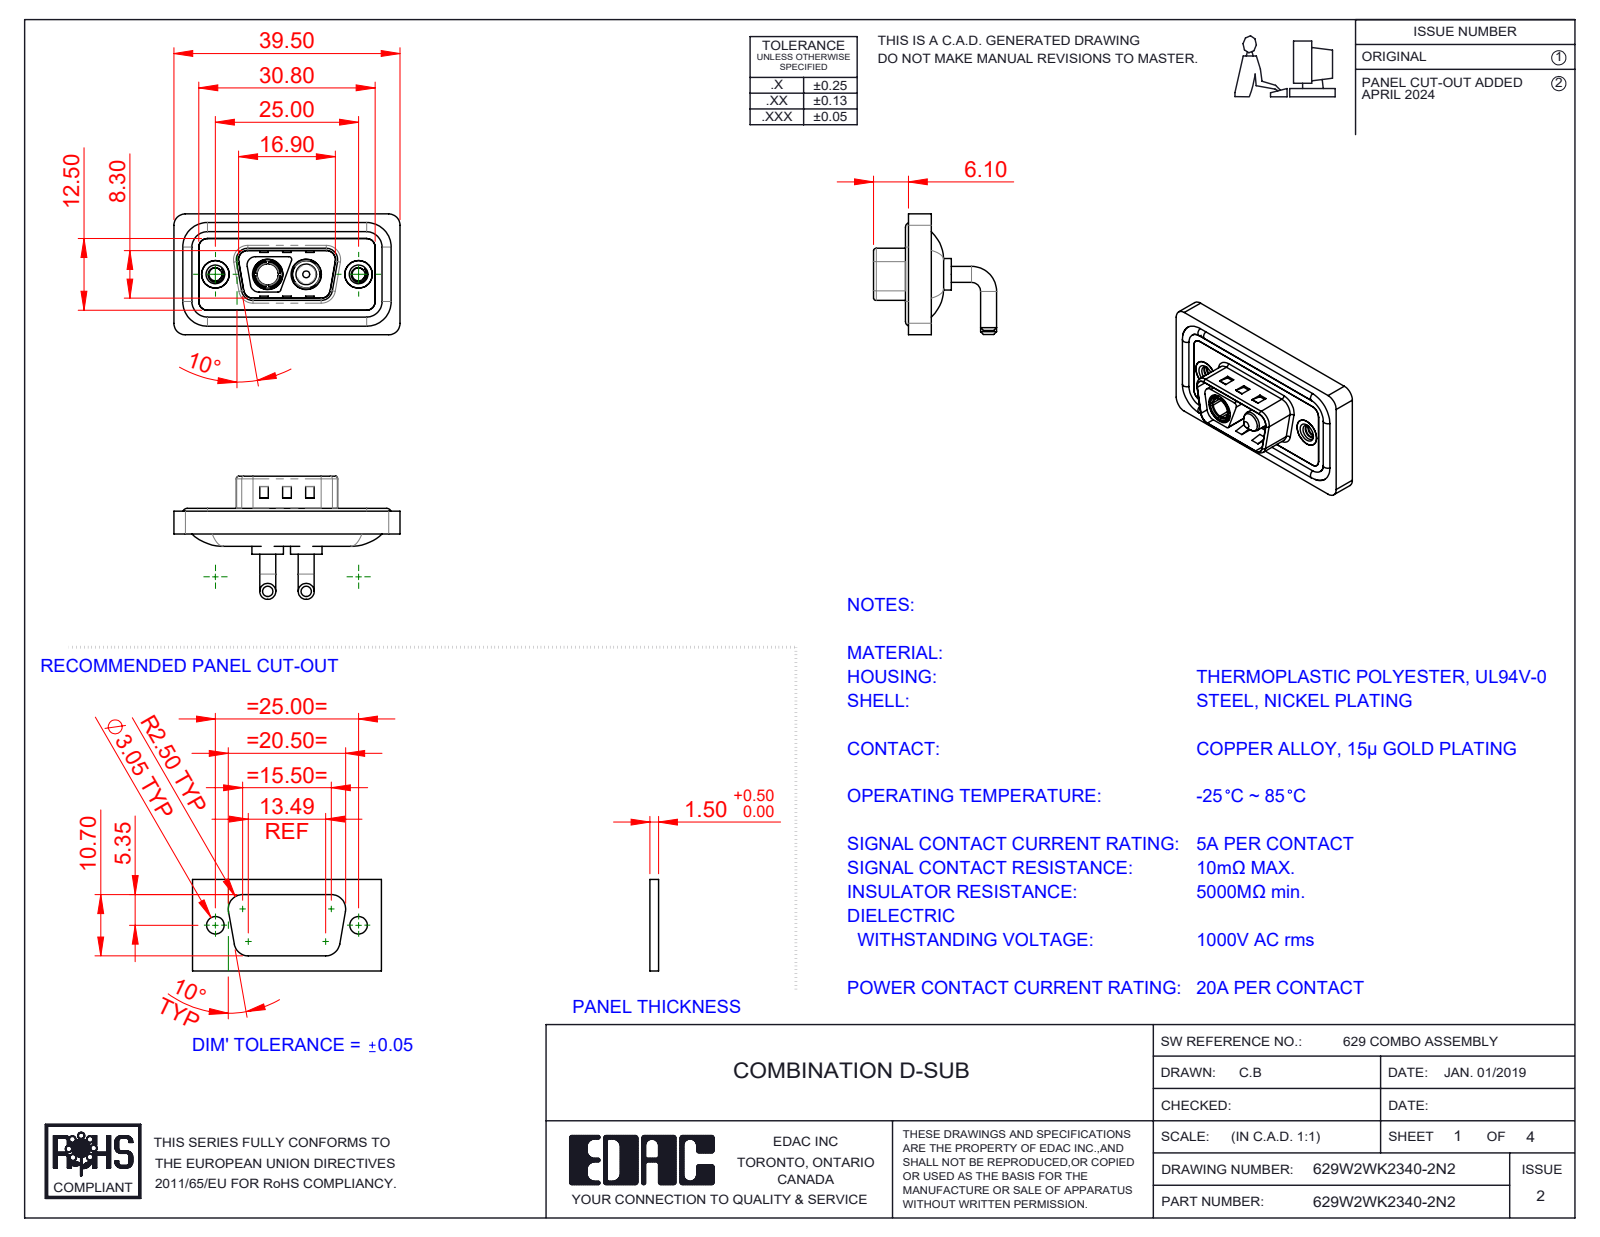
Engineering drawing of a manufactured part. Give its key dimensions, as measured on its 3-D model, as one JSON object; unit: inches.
{"part_name": "629W2WK2340-2N2; 629Combo Threaded Rivet_2; Power Pin_20A RA; 629Combo Waterproof Housing_09 Contacts (+4 more)", "step_written_by": "SolidWorks 2023 (CONFIG_CONTROL_DESIGN)", "units": "inches", "bodies": {"solids": 11, "faces": 542, "planar": 189, "cylindrical": 231, "other": 122}, "overall_size": [1.555, 0.846, 0.831], "volume_in3": 0.286, "surface_area_in2": 11.67, "round_holes": [[0.089, 2], [0.157, 2], [0.189, 2], [0.191, 2], [0.197, 2], [0.209, 2], [0.146, 1]], "round_bosses_or_shafts": [[0.11, 4], [0.063, 4], [0.217, 2], [0.205, 2], [0.193, 2], [0.187, 2], [0.148, 2], [0.195, 1]], "partial_cylinders_radius": [[0.059, 20], [0.079, 18], [0.02, 10], [0.063, 8], [0.01, 4], [0.024, 4], [0.026, 4], [0.035, 4]], "face_to_face_distances": [0.016, 0.114, 0.043, 0.031, 0.083, 0.098, 0.122, 0.063, 0.177, 0.059], "hole_center_spacings": [0.36, 0.624, 0.265, 0.984]}
